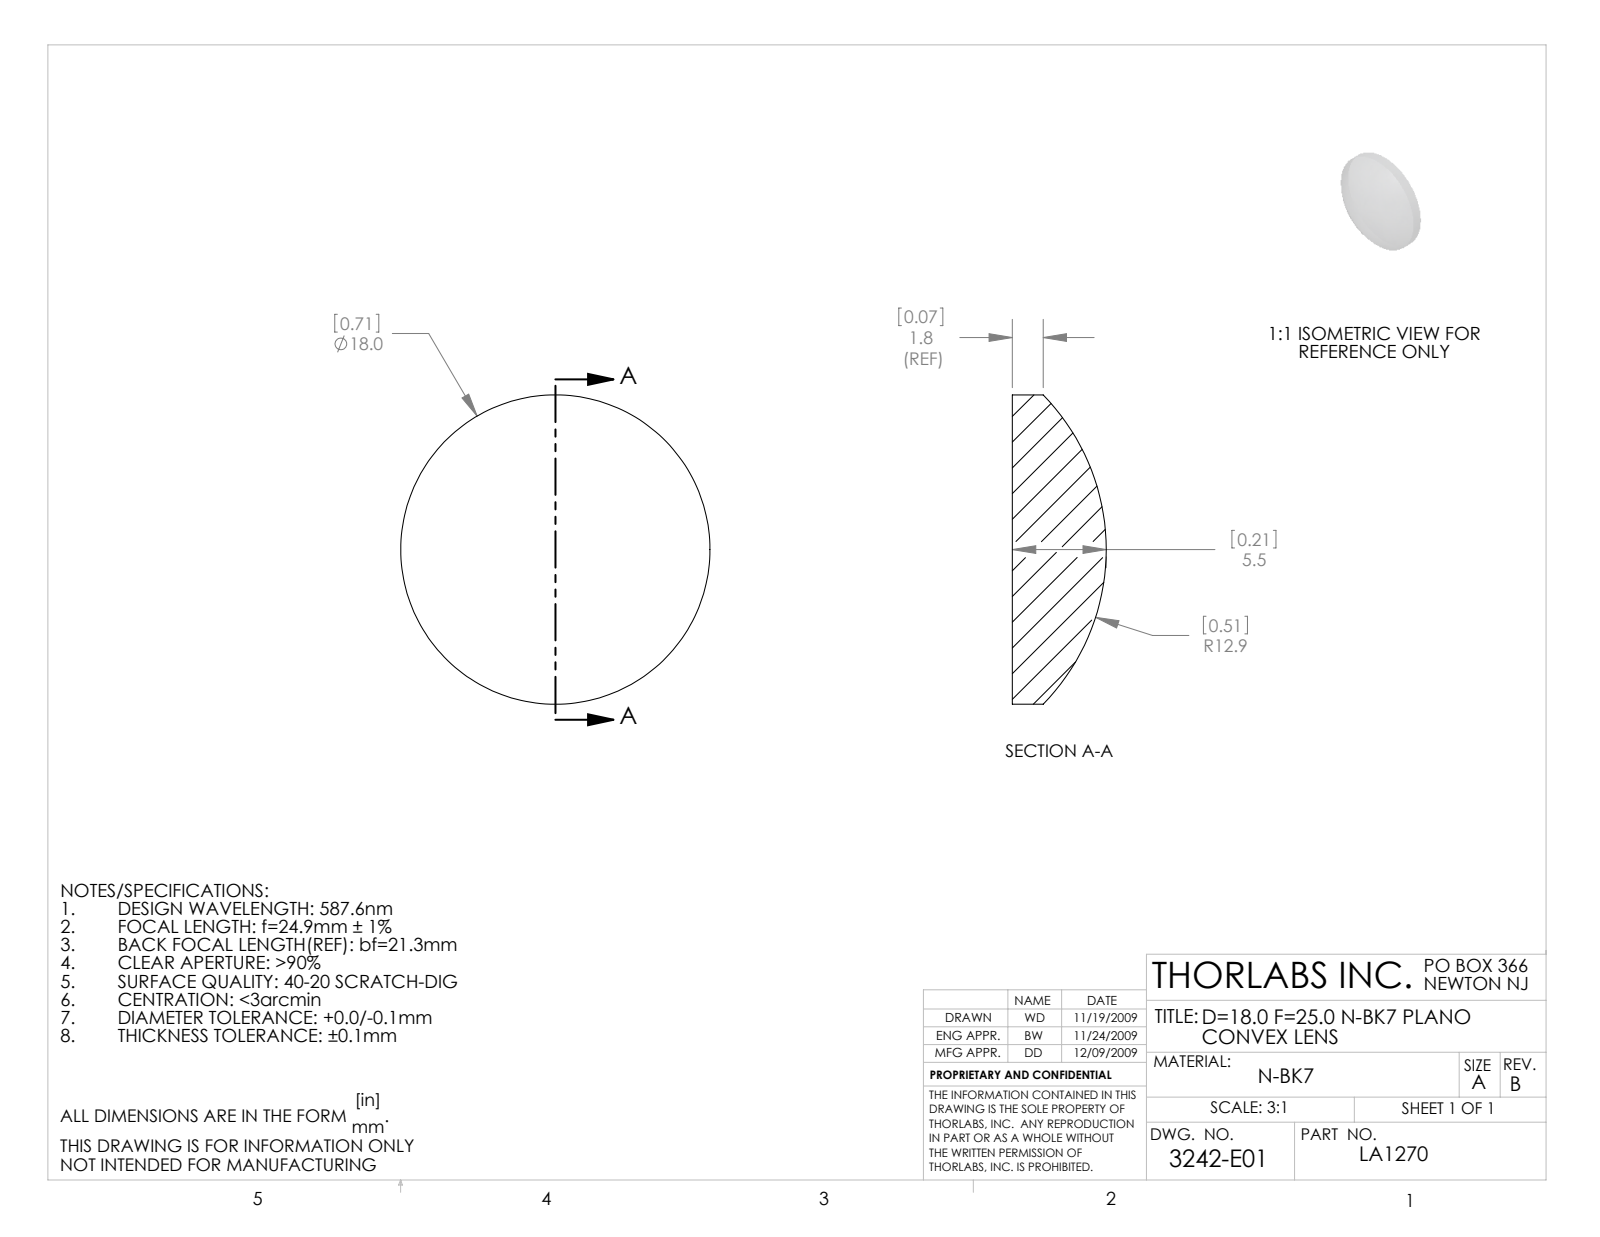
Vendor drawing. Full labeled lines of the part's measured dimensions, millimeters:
Part name (STEP PRODUCT): 3242-E0W
STEP written by: SolidWorks 2009 (AUTOMOTIVE_DESIGN)
Units: millimetres
Bodies: 1 solid, 5 faces (1 planar, 2 cylindrical, 2 other)
Overall size (bounding box): 18 × 18 × 5.46
Volume: 948 mm³ · Surface area: 652 mm²
Round bosses / shafts (diameter × count): ⌀18 ×1
